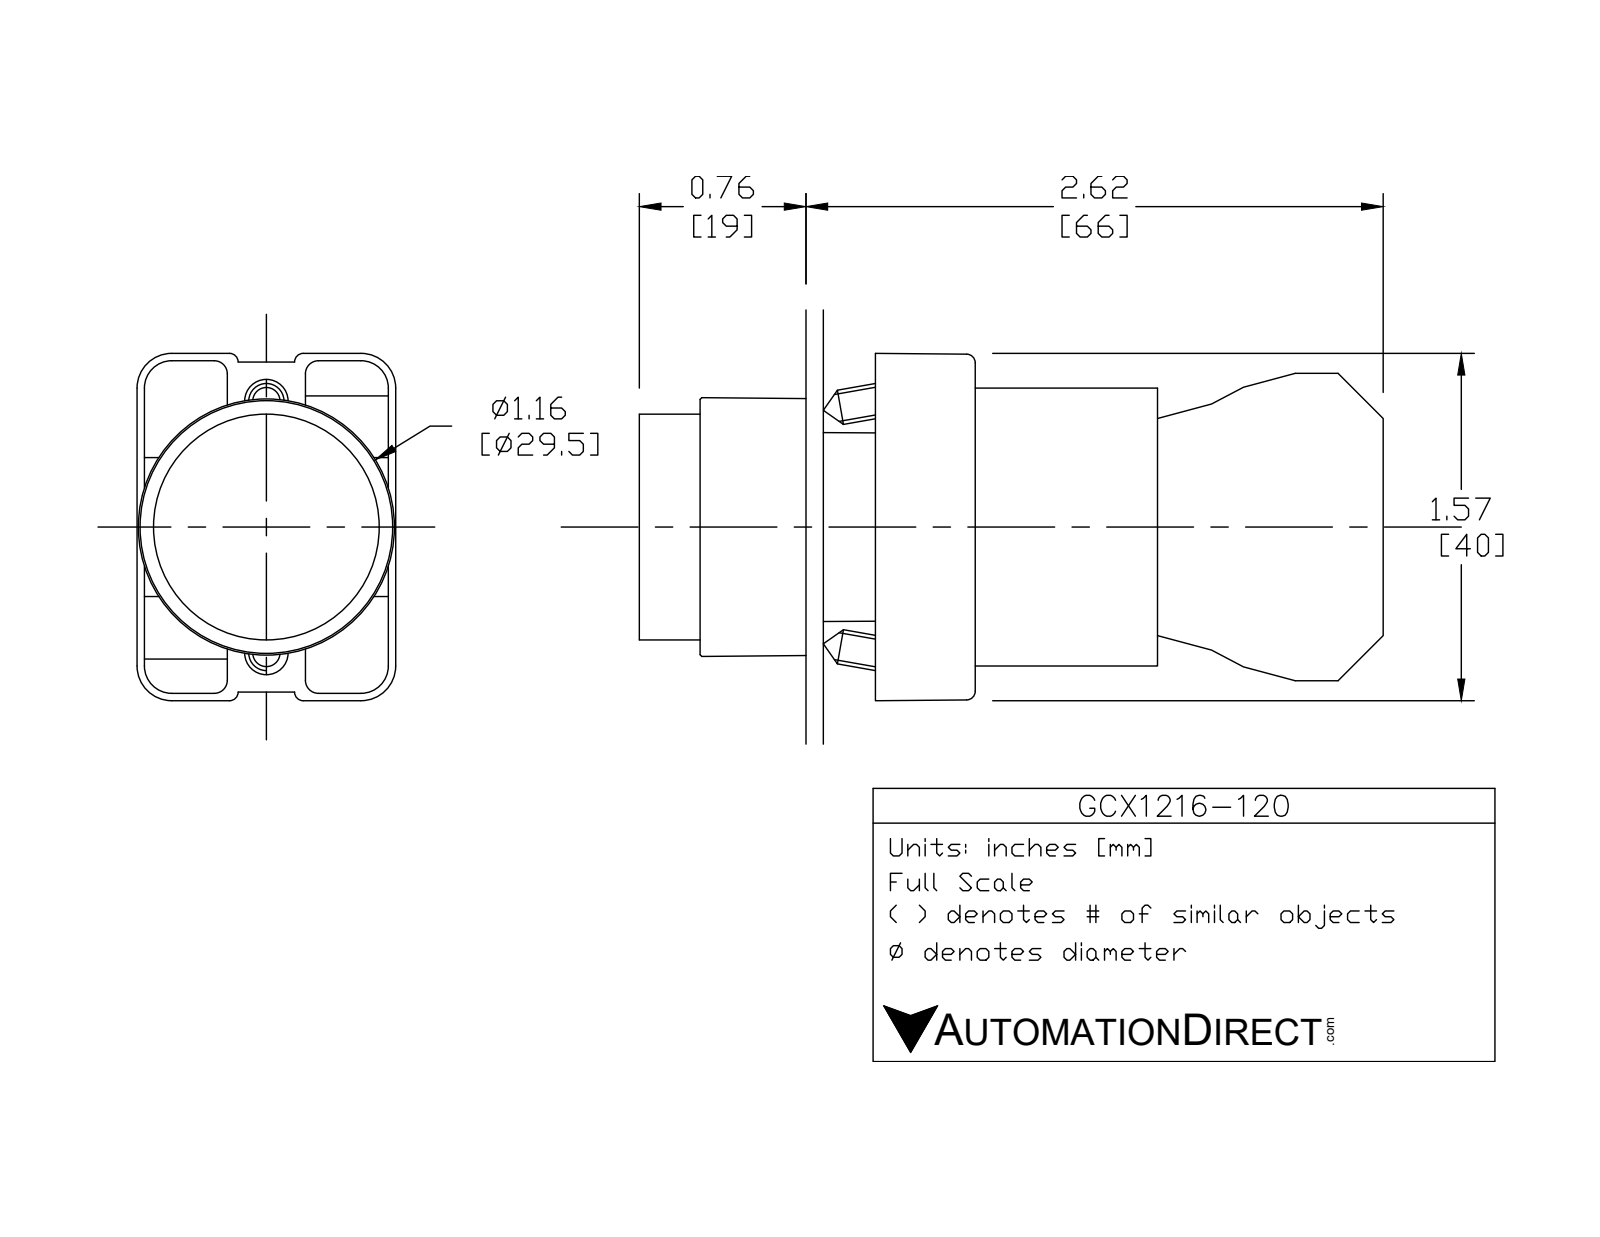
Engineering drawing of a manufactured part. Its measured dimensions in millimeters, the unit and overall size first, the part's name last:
Units: millimetres
Overall size (bounding box): 84.3 × 40.2 × 29.9
Round holes (diameter × count): ⌀2 ×2, ⌀3.1 ×2, ⌀3.3 ×2, ⌀2.2 ×1, ⌀5 ×1, ⌀11.9 ×1, ⌀22.3 ×1, ⌀22.6 ×1, ⌀26 ×1
Round bosses / shafts (diameter × count): ⌀4 ×4, ⌀29.8 ×1, ⌀25.5 ×1, ⌀24 ×1, ⌀21.7 ×1, ⌀19.8 ×1, ⌀12.8 ×1
Partial cylindrical surfaces — rounded edges, fillets, slot ends (radius × count): R1.5 ×24, R1 ×12, R3.1 ×12, R4 ×12, R1 ×8, R3.3 ×2, R0.5 ×1, R1.6 ×1
Main face-to-face distances: 21, 14.7, 29.7, 51.3, 30.3, 0.8, 0.8, 14.6, 29.6, 15.1
Hole centre spacings: 6, 13.8, 12, 12.4
Volume: 44 590 mm³ · Surface area: 23 430 mm²
Bodies: 7 solids, 425 faces (250 planar, 144 cylindrical, 31 other)
Part name (STEP PRODUCT): ECX1050; ecx1029; ecx1040; GCX1216-120 (+1 more)
STEP written by: SolidWorks 2016 (AUTOMOTIVE_DESIGN)
